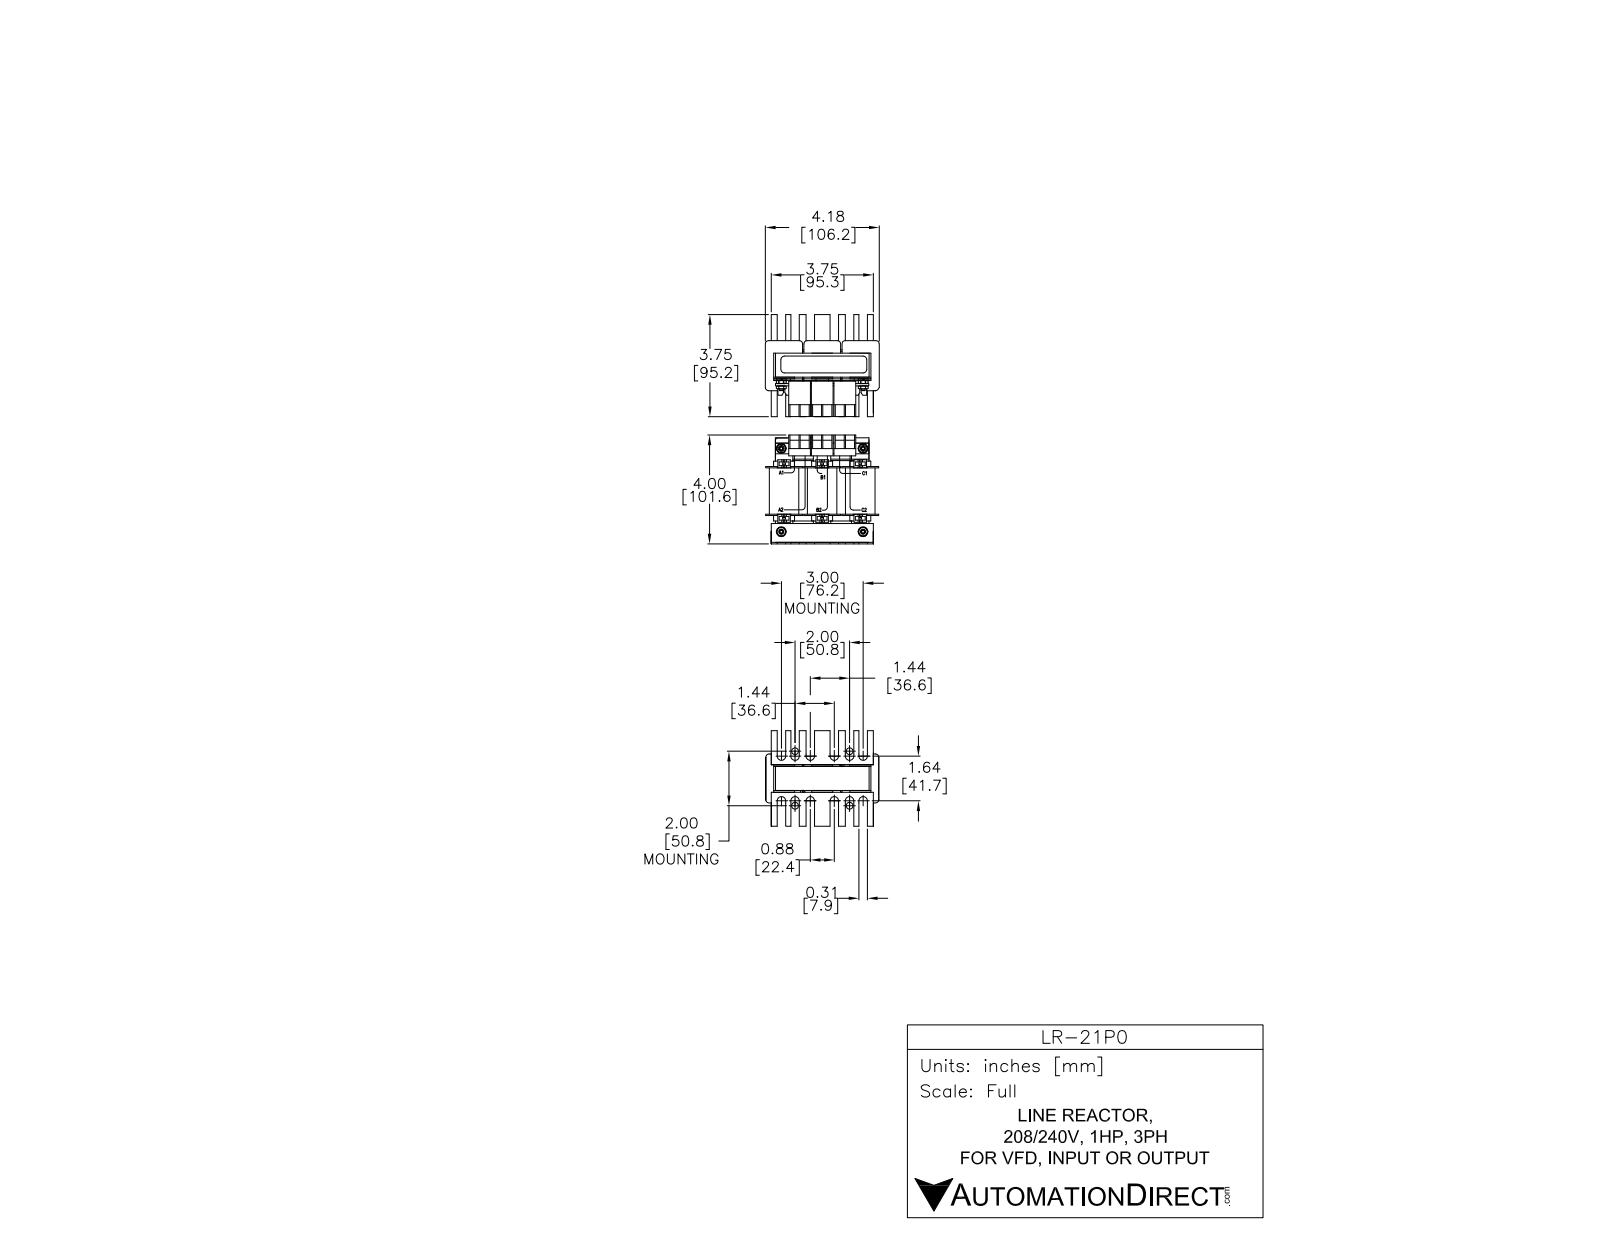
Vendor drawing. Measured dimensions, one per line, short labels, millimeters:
name: LR-21P0
written by: SolidWorks 2011 (AUTOMOTIVE_DESIGN)
unit: mm
bodies: 17 solids, 941 faces (743 planar, 198 cylindrical, 0 other)
size: 105.25 × 98.41 × 89.25
volume: 272 326 mm³; area: 99 223 mm²
bosses: 4× ⌀7.75, 4× ⌀3.5
rounds: 50× R4, 24× R1.82, 12× R8, 6× R3, 3× R0.86, 2× R1.25
face distances: 5, 21.5, 2.75, 51, 26.25, 26.5, 7.5, 29, 71, 2.5
